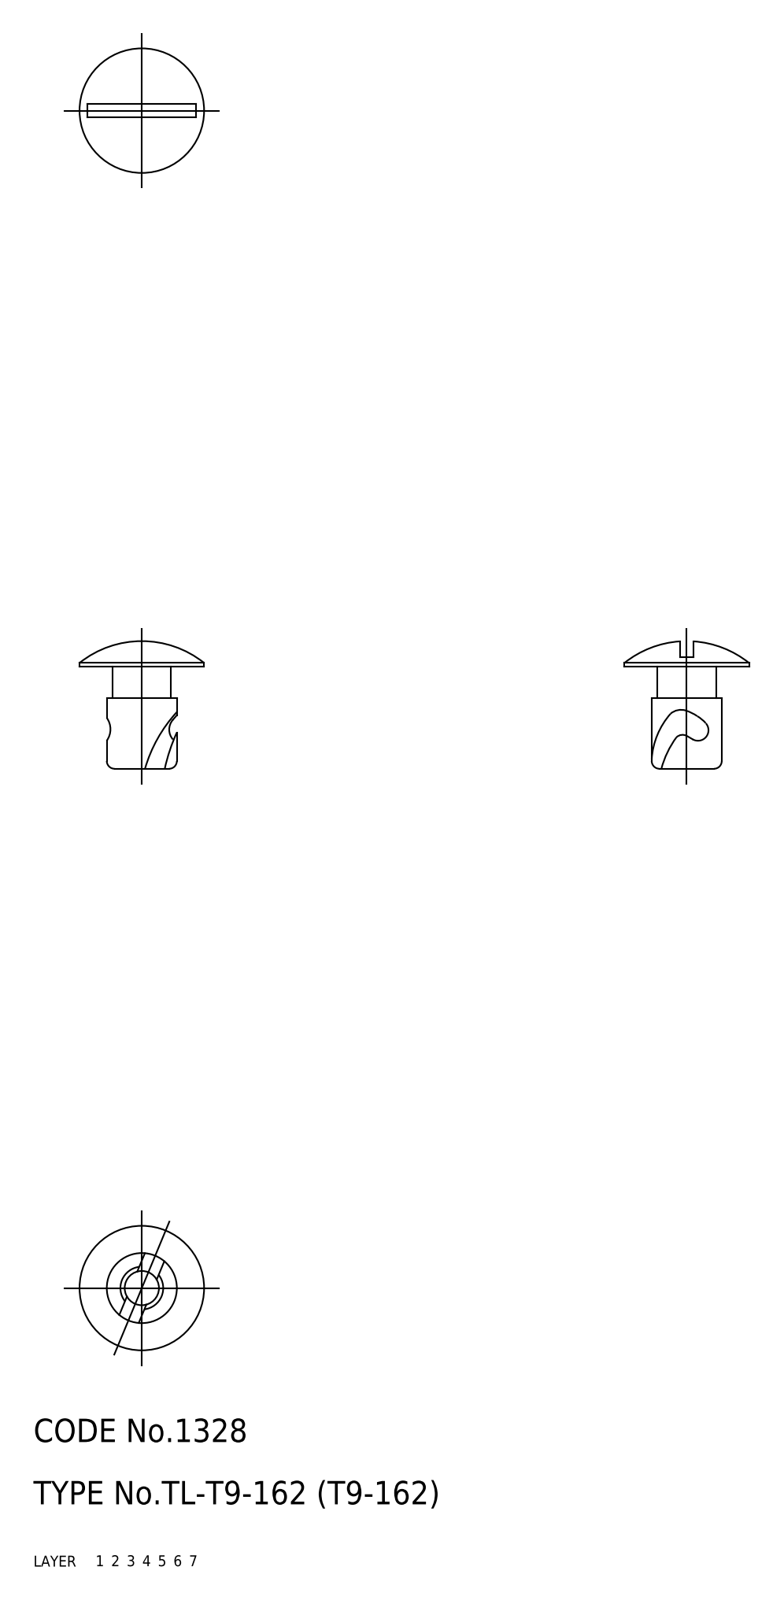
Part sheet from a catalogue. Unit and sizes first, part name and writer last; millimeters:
Units: millimetres
Overall size (bounding box): 16.37 × 16 × 16
Volume: 854 mm³ · Surface area: 981 mm²
Bodies: 1 solid, 32 faces (0 planar, 0 cylindrical, 32 other)
Part name (STEP PRODUCT): fastener
STEP written by: CADfix (AUTOMOTIVE_DESIGN)
